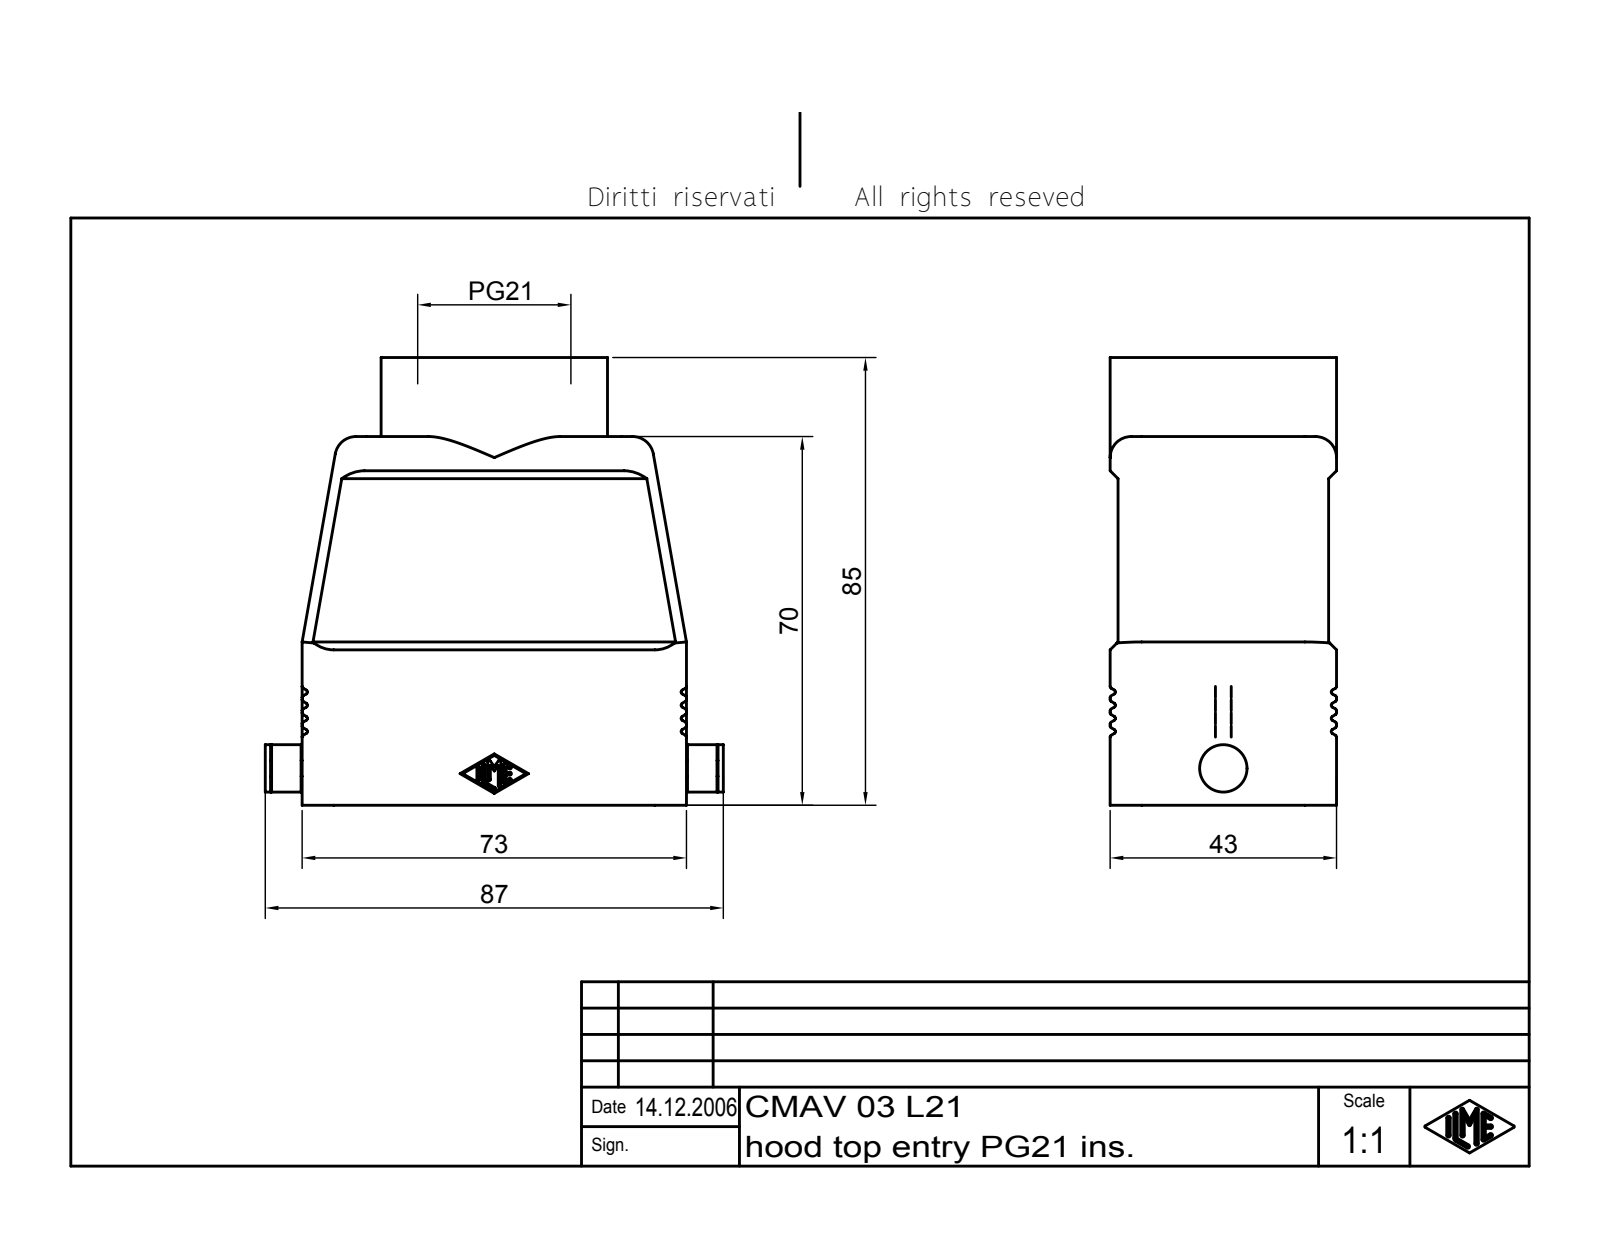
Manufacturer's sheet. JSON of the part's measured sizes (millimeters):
{"part_name": "CMAV 03 L21", "step_written_by": "Autodesk Inventor 7 (AUTOMOTIVE_DESIGN)", "units": "millimeters", "bodies": {"solids": 1, "faces": 643, "planar": 129, "cylindrical": 312, "other": 202}, "overall_size": [87, 85, 43], "volume_mm3": 66037, "surface_area_mm2": 41168, "round_holes": [[25, 1], [26.78, 1]], "round_bosses_or_shafts": [[43, 1], [9, 1], [3, 1]], "partial_cylinders_radius": [[0.4, 64], [0.25, 14], [3, 8], [6, 8], [2, 4], [4, 4], [5, 2]], "face_to_face_distances": [1.5, 3, 40, 38.5, 37, 41.5, 70, 67, 43, 8.5]}
